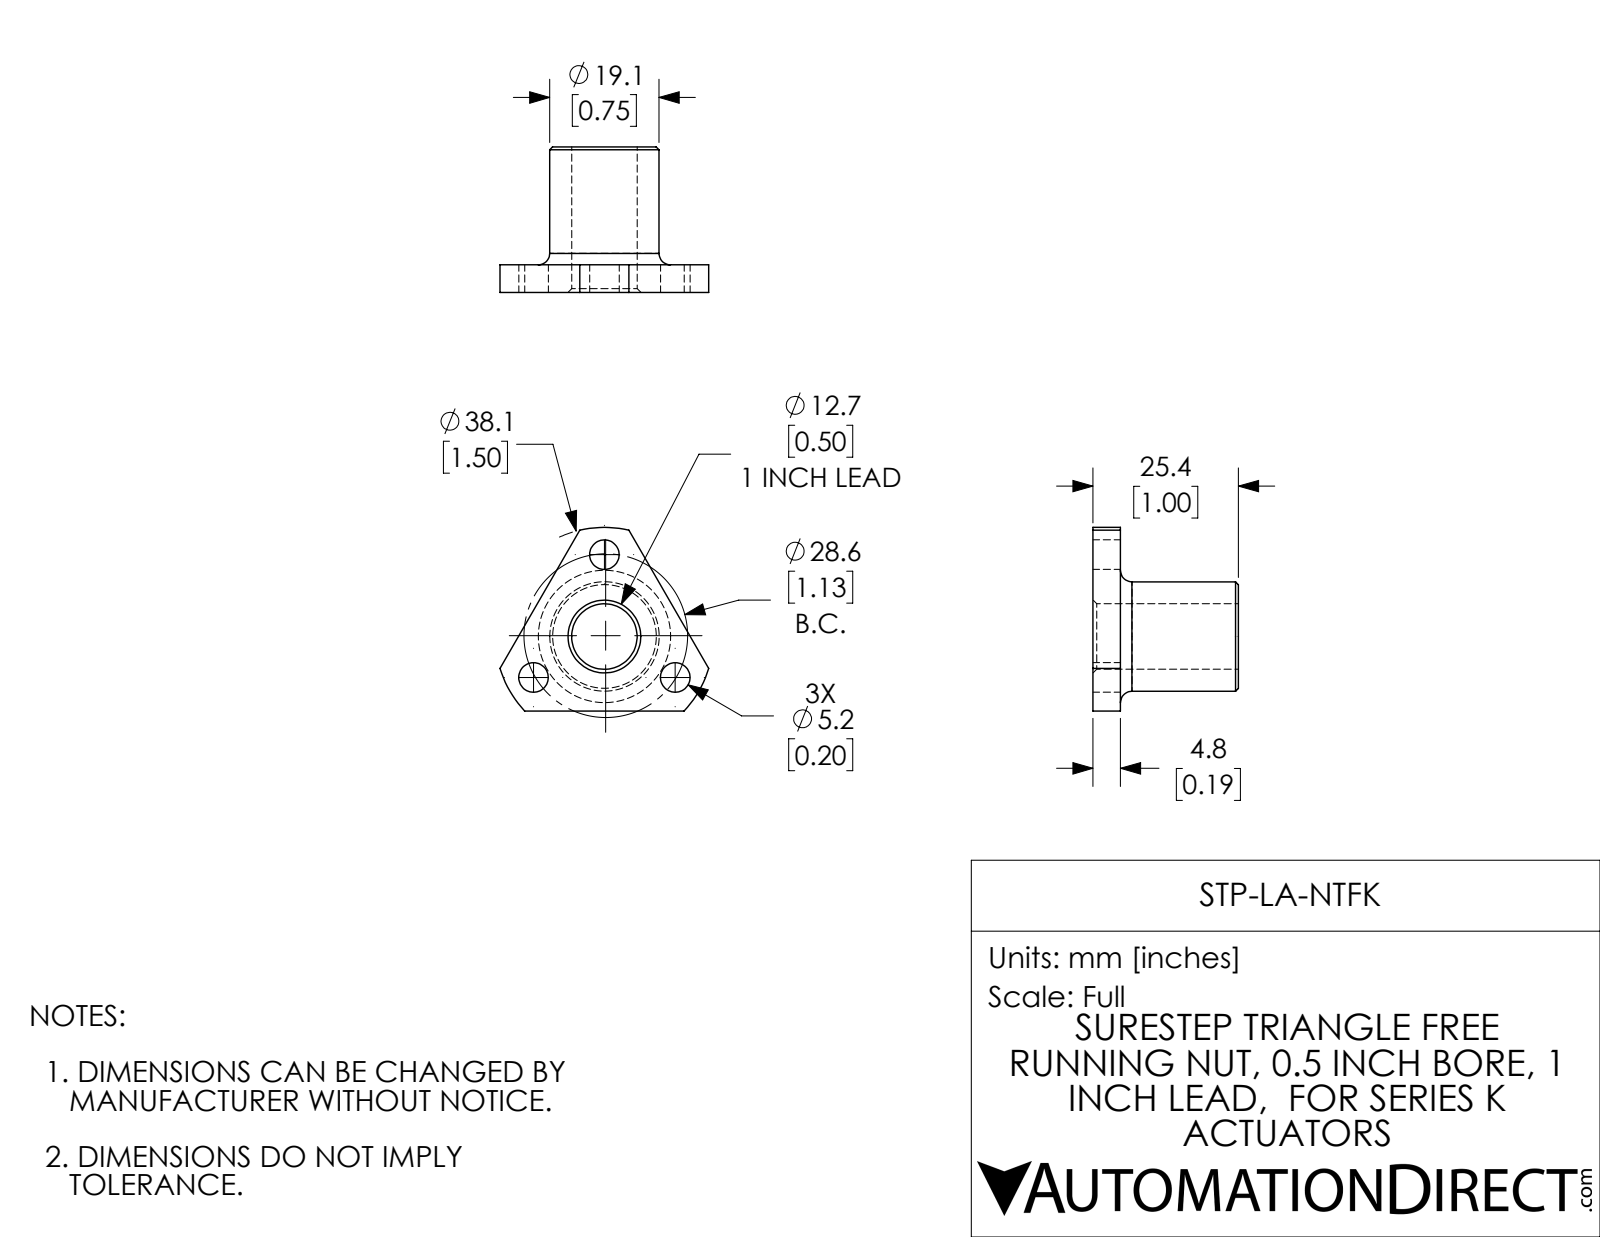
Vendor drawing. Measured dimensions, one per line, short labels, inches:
name: STP-LA-NTFK
written by: SolidWorks 2017 (AUTOMOTIVE_DESIGN)
unit: in
bodies: 1 solid, 25 faces (6 planar, 13 cylindrical, 6 other)
size: 1.435 × 1.262 × 1
volume: 0.417 in³; area: 6.32 in²
holes: 3× ⌀0.203, 1× ⌀0.45
bosses: 1× ⌀0.752
rounds: 1× R0.75
face distances: 0.189, 0.811, 1
hole spacings: 0.563, 0.974, 0.563, 0.975
